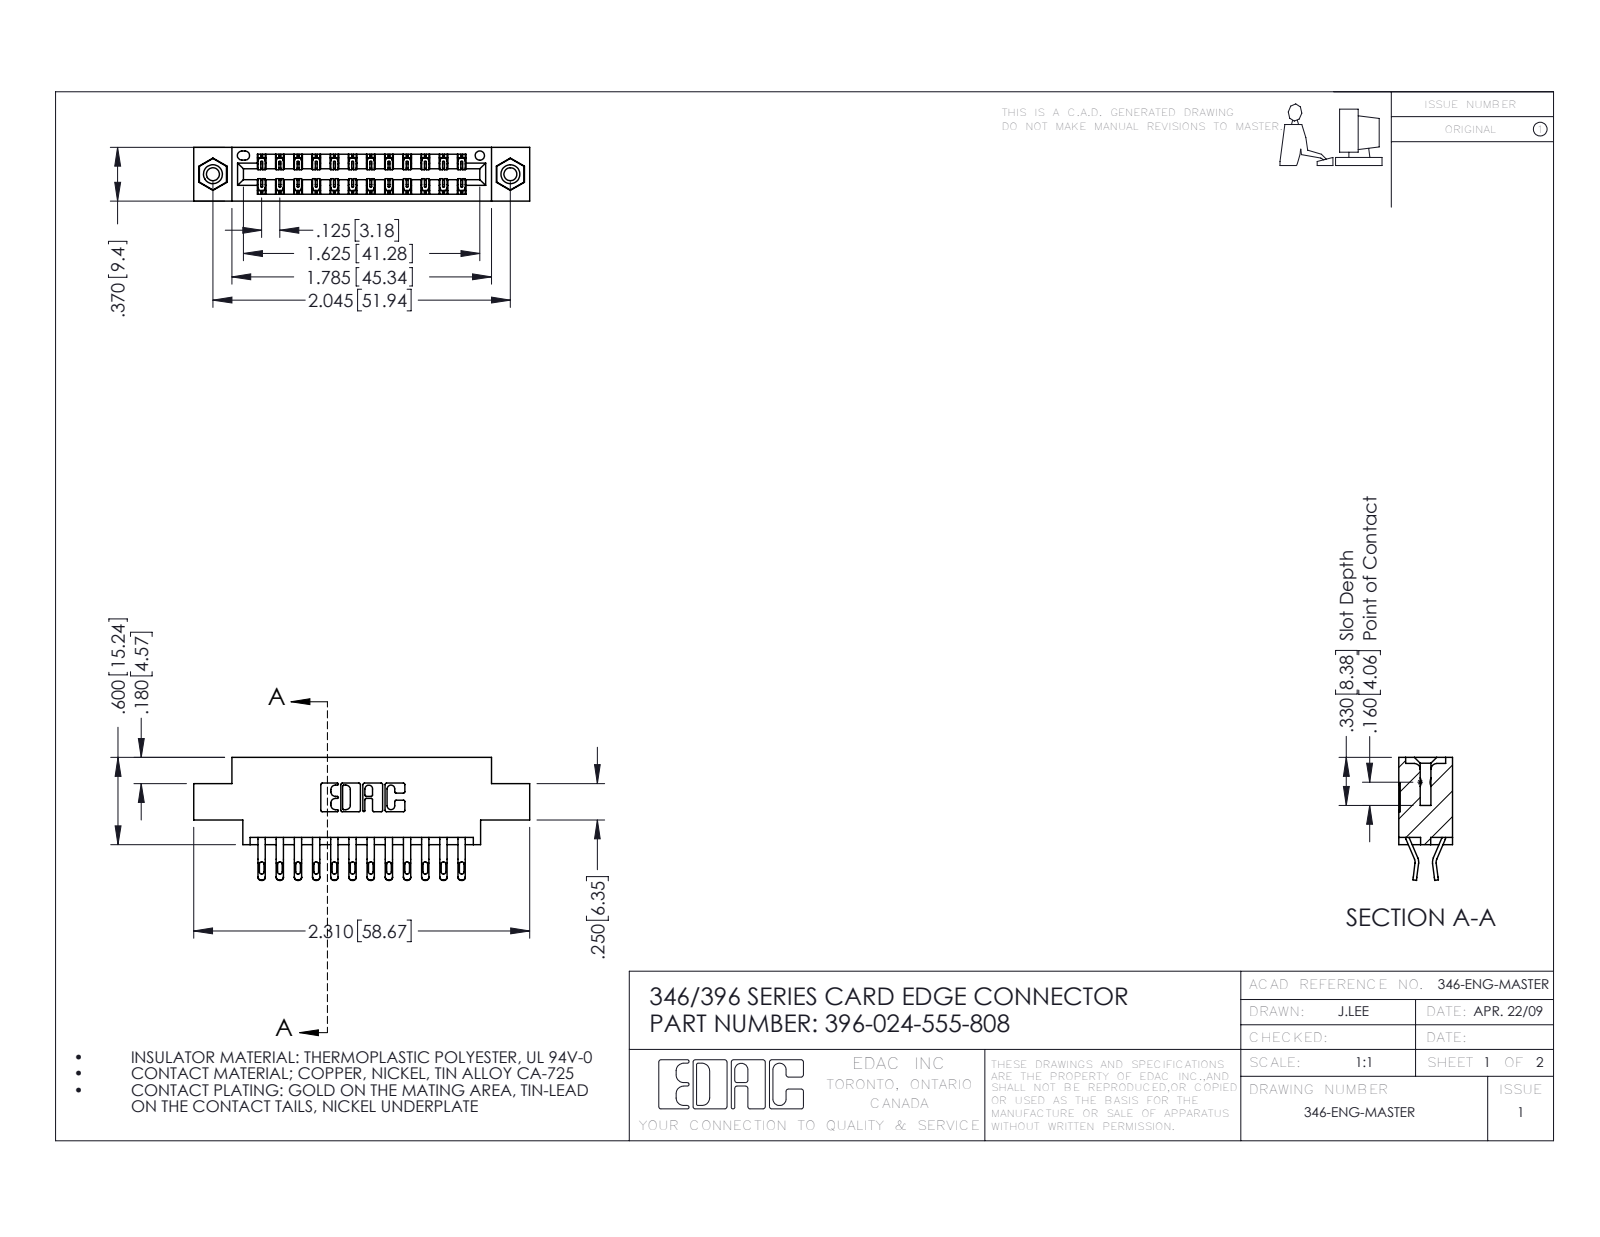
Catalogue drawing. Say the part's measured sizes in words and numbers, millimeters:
The part is named "346 Part_0.170 Offset - 0.156 Dia-TI; 396-024-555-808; 345-292-001_555 Tail; 345-250-001_345-250-003-102". Its 3-D file was written by "SolidWorks 2016 (CONFIG_CONTROL_DESIGN)". It is 27 solids with 1578 faces: 904 planar, 658 cylindrical and 16 other. Overall it measures 58.7 by 21.5 by 9.4 millimeters. Its volume is 5 390 cubic millimeters and its surface area 7 394 square millimeters. Round holes: 2 of diameter 2.3, 2 of diameter 3.2, 2 of diameter 4, 1 of diameter 1.6. Round bosses or shafts: 2 of diameter 3.9. Partial cylindrical surfaces (rounded edges, fillets, slot ends): 48 of radius 0.4, 48 of radius 0.5, 36 of radius 0.2, 22 of radius 0.3, 6 of radius 0.2, 6 of radius 0.8, 3 of radius 0.7, 2 of radius 0.3. The main face-to-face distances are 6.4, 1.2, 8.2, 9.4, 0.6, 5.6, 3.8, 1.8, 7.6, 7. The hole center spacings are 6.2, 46.7, 51.9.
